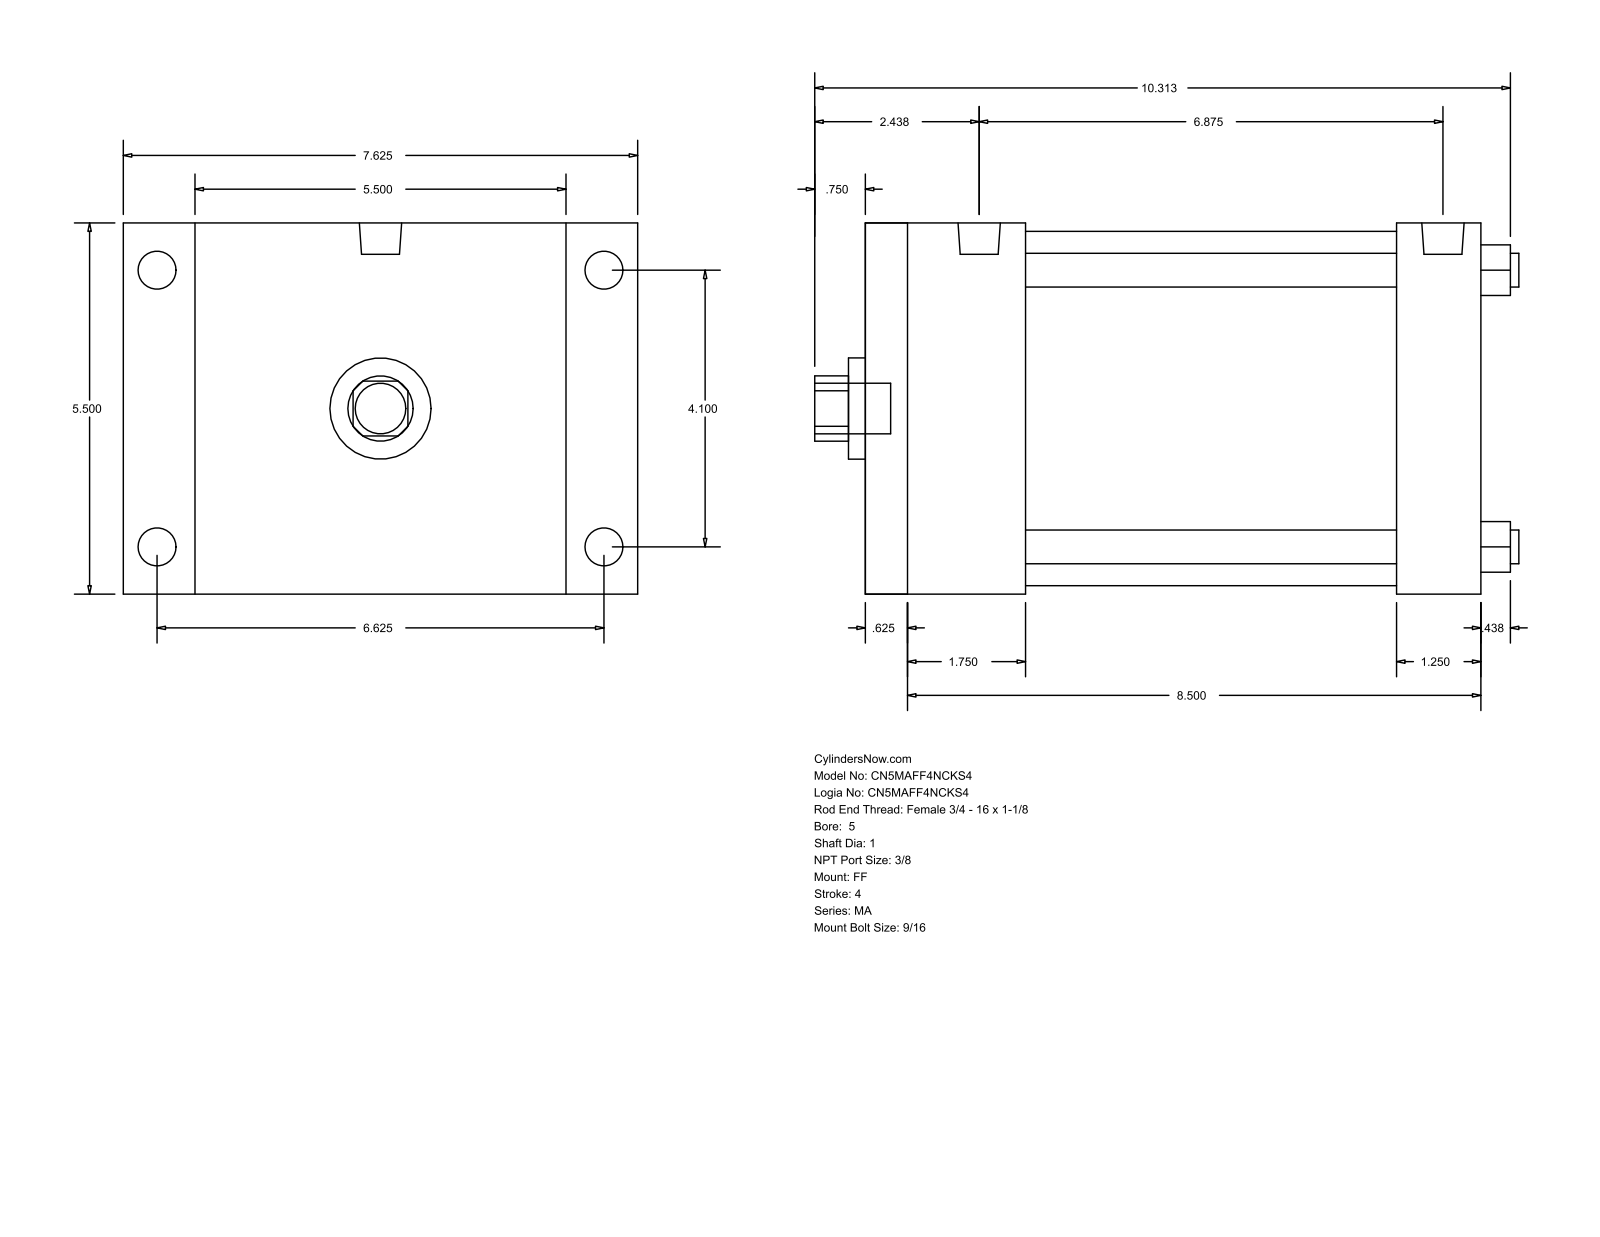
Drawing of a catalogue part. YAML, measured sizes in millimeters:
part_name: "MA_FF__0500_1"
step_written_by: "GSSL Pune (CONFIG_CONTROL_DESIGN)"
units: millimeters
bodies: {solids: 0, faces: 92, planar: 64, cylindrical: 28, other: 0}
overall_size: [265.11, 193.68, 139.7]
round_holes:
  - {diameter: 12.7, count: 4}
  - {diameter: 25.4, count: 1}
  - {diameter: 38.1, count: 1}
  - {diameter: 133.35, count: 1}
round_bosses_or_shafts:
  - {diameter: 14.29, count: 4}
  - {diameter: 11.11, count: 4}
  - {diameter: 15.93, count: 2}
  - {diameter: 19.05, count: 1}
partial_cylinders:
  - {radius: 12.29, count: 1}
face_to_face_distances: [139.7, 231.77, 15.87, 215.9, 200.02, 184.15, 31.75, 60.33, 44.46, 139.69]
hole_center_spacings: [73.64, 104.14, 147.28]
